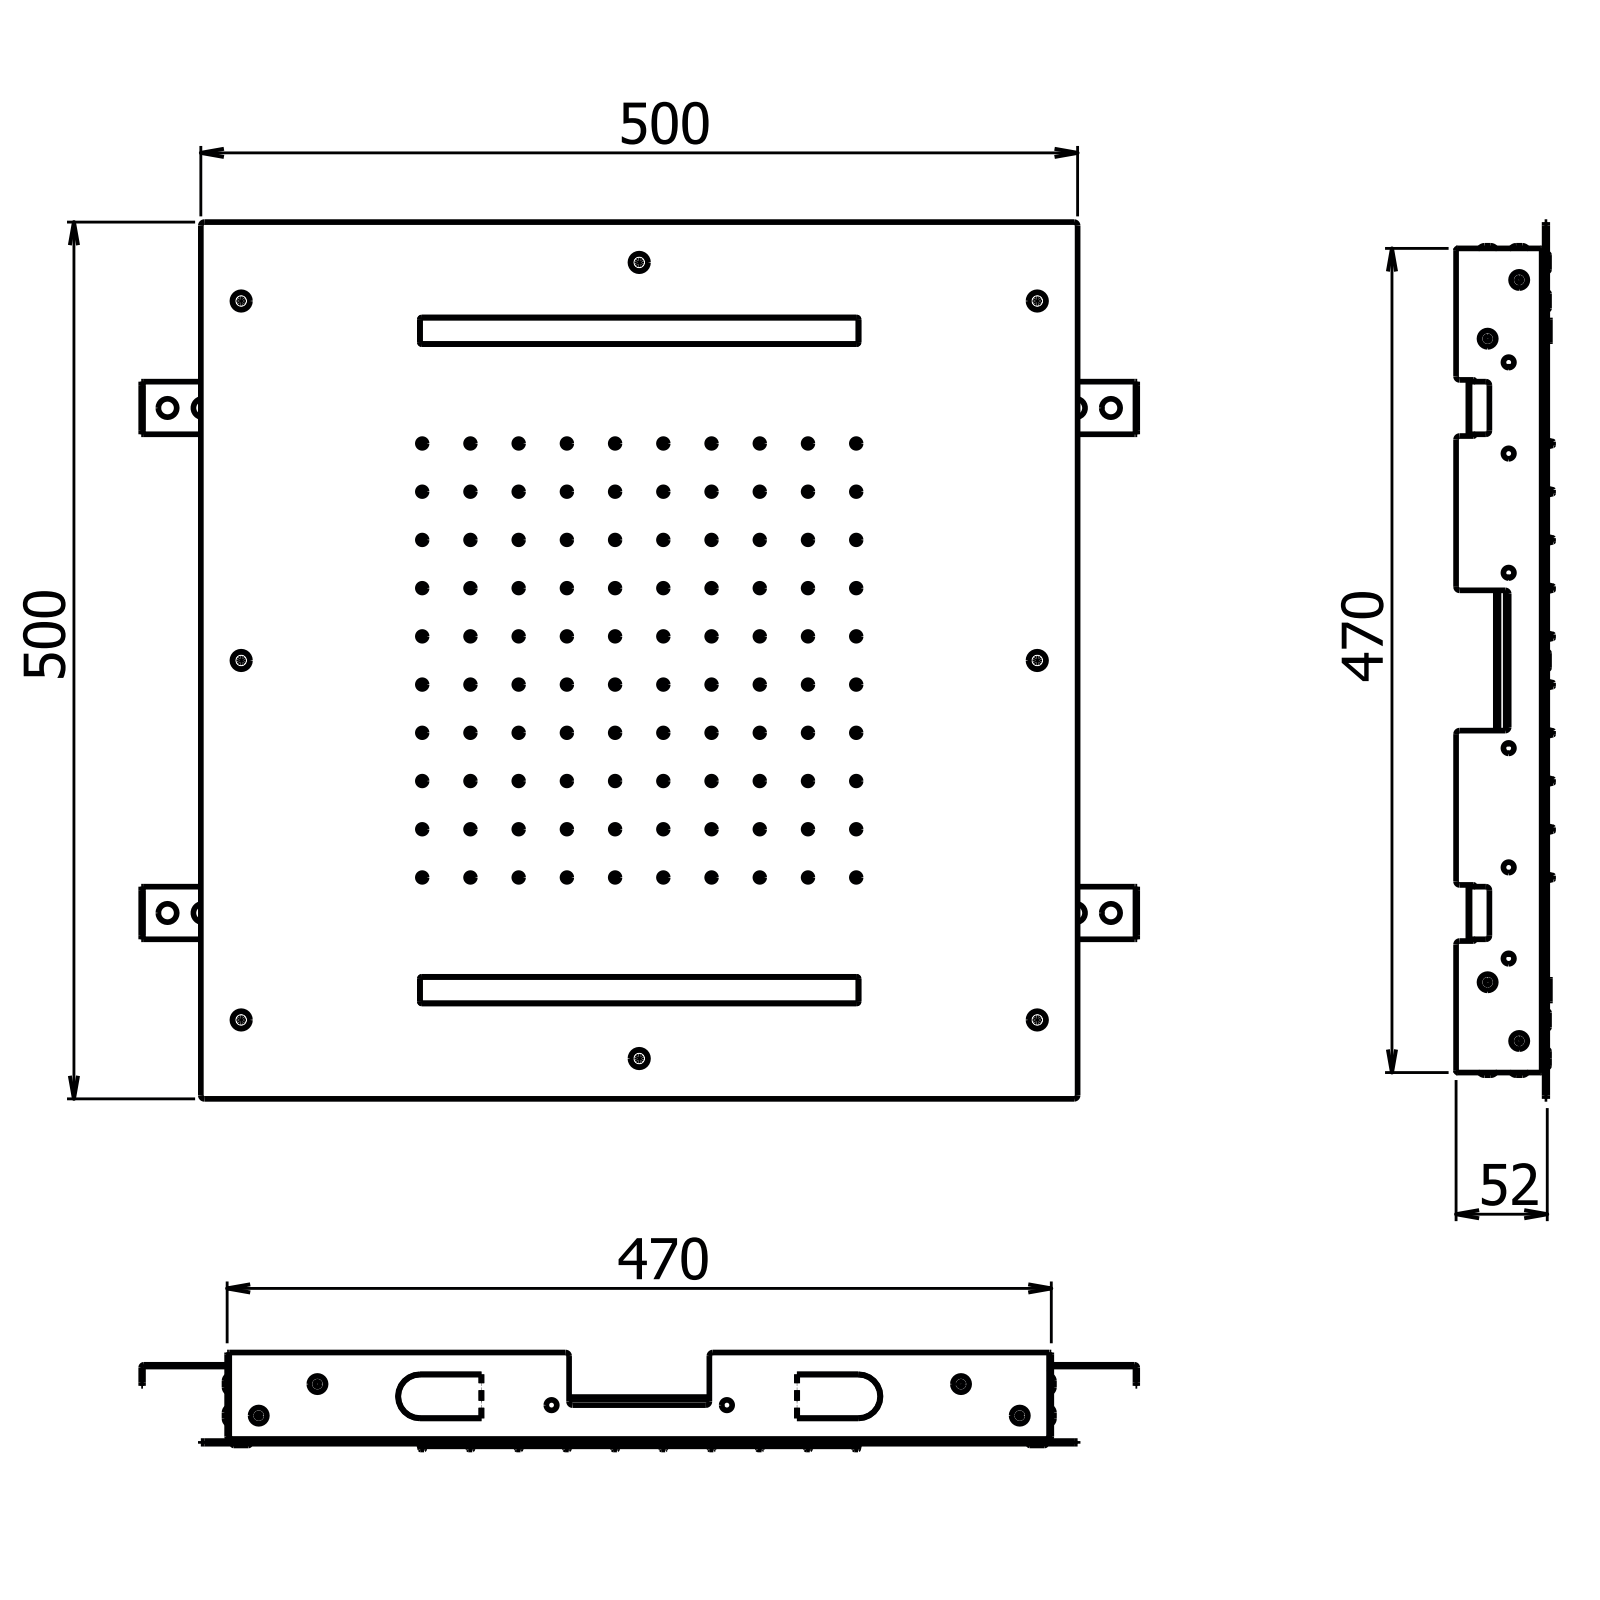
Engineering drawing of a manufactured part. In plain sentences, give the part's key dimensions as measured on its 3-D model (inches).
The part is named "A.R._24569/20220905". Its 3-D file was written by "Spatial InterOp 3D (AUTOMOTIVE_DESIGN)". It is 1 solid with 4124 faces: 1475 planar, 1259 cylindrical and 1390 other. Overall it measures 22.362 by 19.685 by 2.177 inches. Its volume is 59.38 cubic inches and its surface area 1 722 square inches. Round holes: 100 of diameter 0.059, 100 of diameter 0.067, 100 of diameter 0.197, 44 of diameter 0.244, 12 of diameter 0.205, 12 of diameter 0.236, 8 of diameter 0.102, 8 of diameter 0.413, 4 of diameter 0.165, 4 of diameter 0.671, 1 of diameter 0.551, 1 of diameter 0.646. Round bosses or shafts: 108 of diameter 0.394, 18 of diameter 0.157, 14 of diameter 0.181, 12 of diameter 0.323, 12 of diameter 0.272, 8 of diameter 0.197, 8 of diameter 0.189, 4 of diameter 0.472. Partial cylindrical surfaces (rounded edges, fillets, slot ends): 203 of radius 0.008, 128 of radius 0.079, 70 of radius 0.02, 54 of radius 0.039, 22 of radius 0.059, 16 of radius 0.004, 8 of radius 0.043, 8 of radius 0.197. The main face-to-face distances are 0.039, 0.098, 0.157, 0.118, 0.059, 0.256, 0.197, 0.02, 0.217, 0.079. The hole center spacings are 5.413, 4.464, 3.424, 1.083, 2.421, 2.165, 4.842, 4.331.
